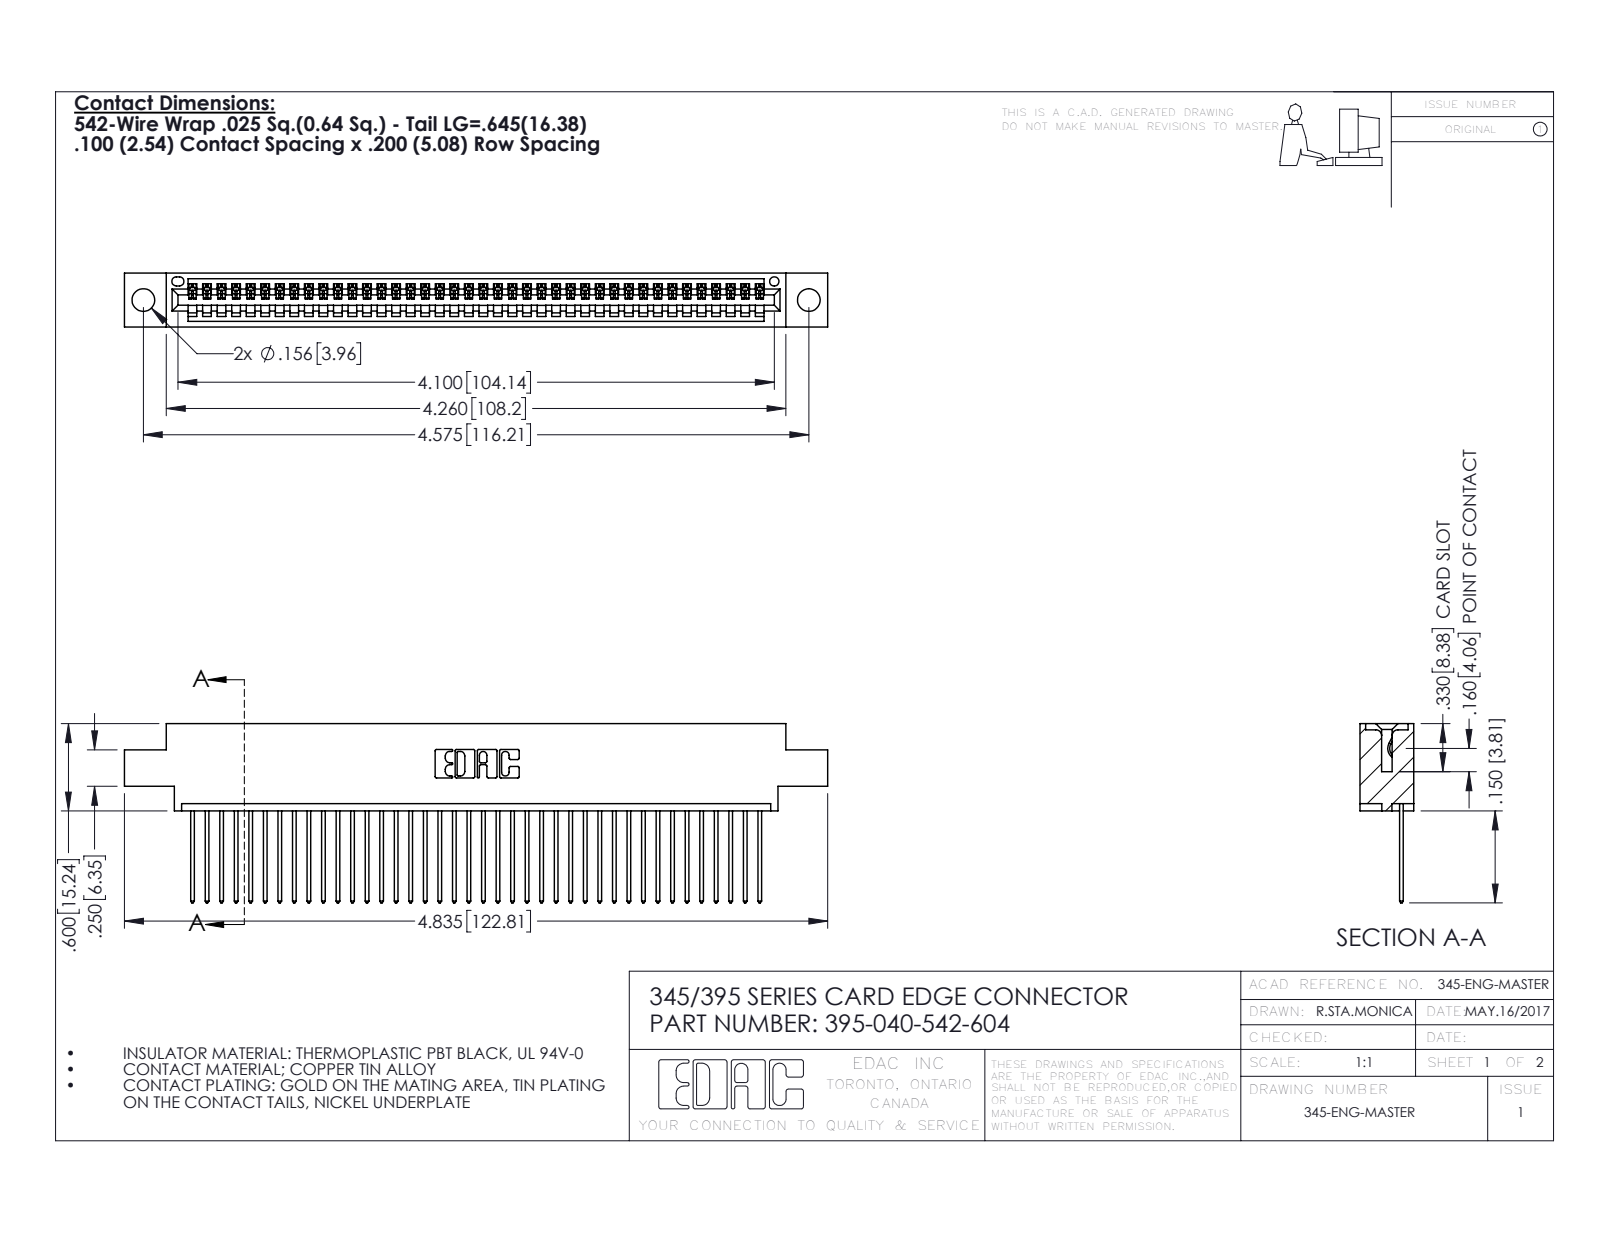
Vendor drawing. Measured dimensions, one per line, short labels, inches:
name: 395-040-542-604; 345 Part_0.170 Offset - 0.156 Dia-TH; 345-292-001_345-293-142
written by: SolidWorks 2016 (CONFIG_CONTROL_DESIGN)
unit: in
bodies: 41 solids, 2450 faces (1684 planar, 766 cylindrical, 0 other)
size: 4.835 × 1.232 × 0.37
volume: 0.704 in³; area: 24.49 in²
holes: 2× ⌀0.156, 1× ⌀0.064
rounds: 80× R0.006, 80× R0.01, 22× R0.01, 6× R0.007, 6× R0.031, 3× R0.026, 2× R0.031, 2× R0.04
face distances: 0.072, 0.298, 0.37, 0.098, 0.272, 0.025, 0.2, 0.225, 0.175, 0.149
hole spacings: 0.27, 4.339, 4.575
